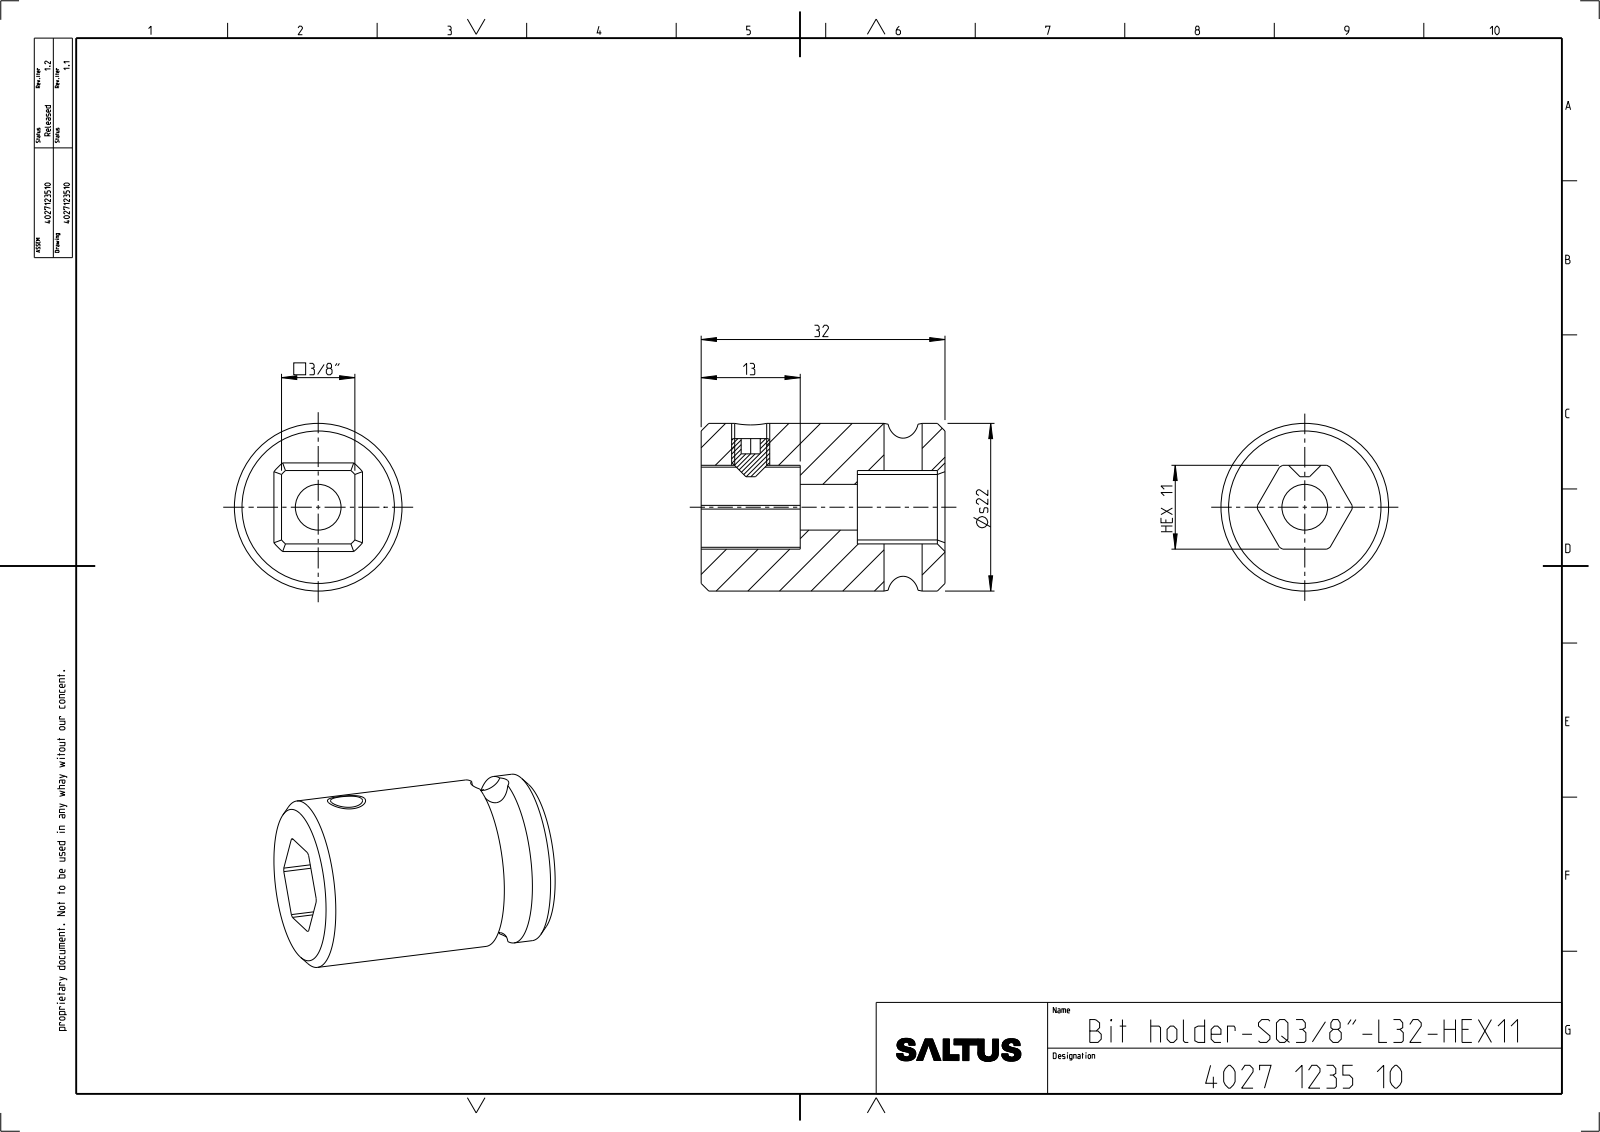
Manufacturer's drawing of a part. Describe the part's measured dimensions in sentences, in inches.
The part is named "4027123510_PART; 4027123510_ASM". Its 3-D file was written by "CREO PARAMETRIC BY PTC INC, 2022414 (CONFIG_CONTROL_DESIGN)". It is 1 solid with 52 faces: 18 planar, 24 cylindrical and 10 other. Overall it measures 1.26 by 0.866 by 0.866 inches. Its volume is 0.541 cubic inches and its surface area 6.431 square inches. Round holes: 2 of diameter 0.197, 1 of diameter 0.165, 1 of diameter 0.236. Round bosses or shafts: 1 of diameter 0.866. Partial cylindrical surfaces (rounded edges, fillets, slot ends): 1 of radius 0.244, 1 of radius 0.254. The main face-to-face distances are 0.433, 1.26, 0.379, 0.027, 0.406, 0.748, 0.512, 0.453, 0.295, 0.807. The hole center spacings are 0.787.
